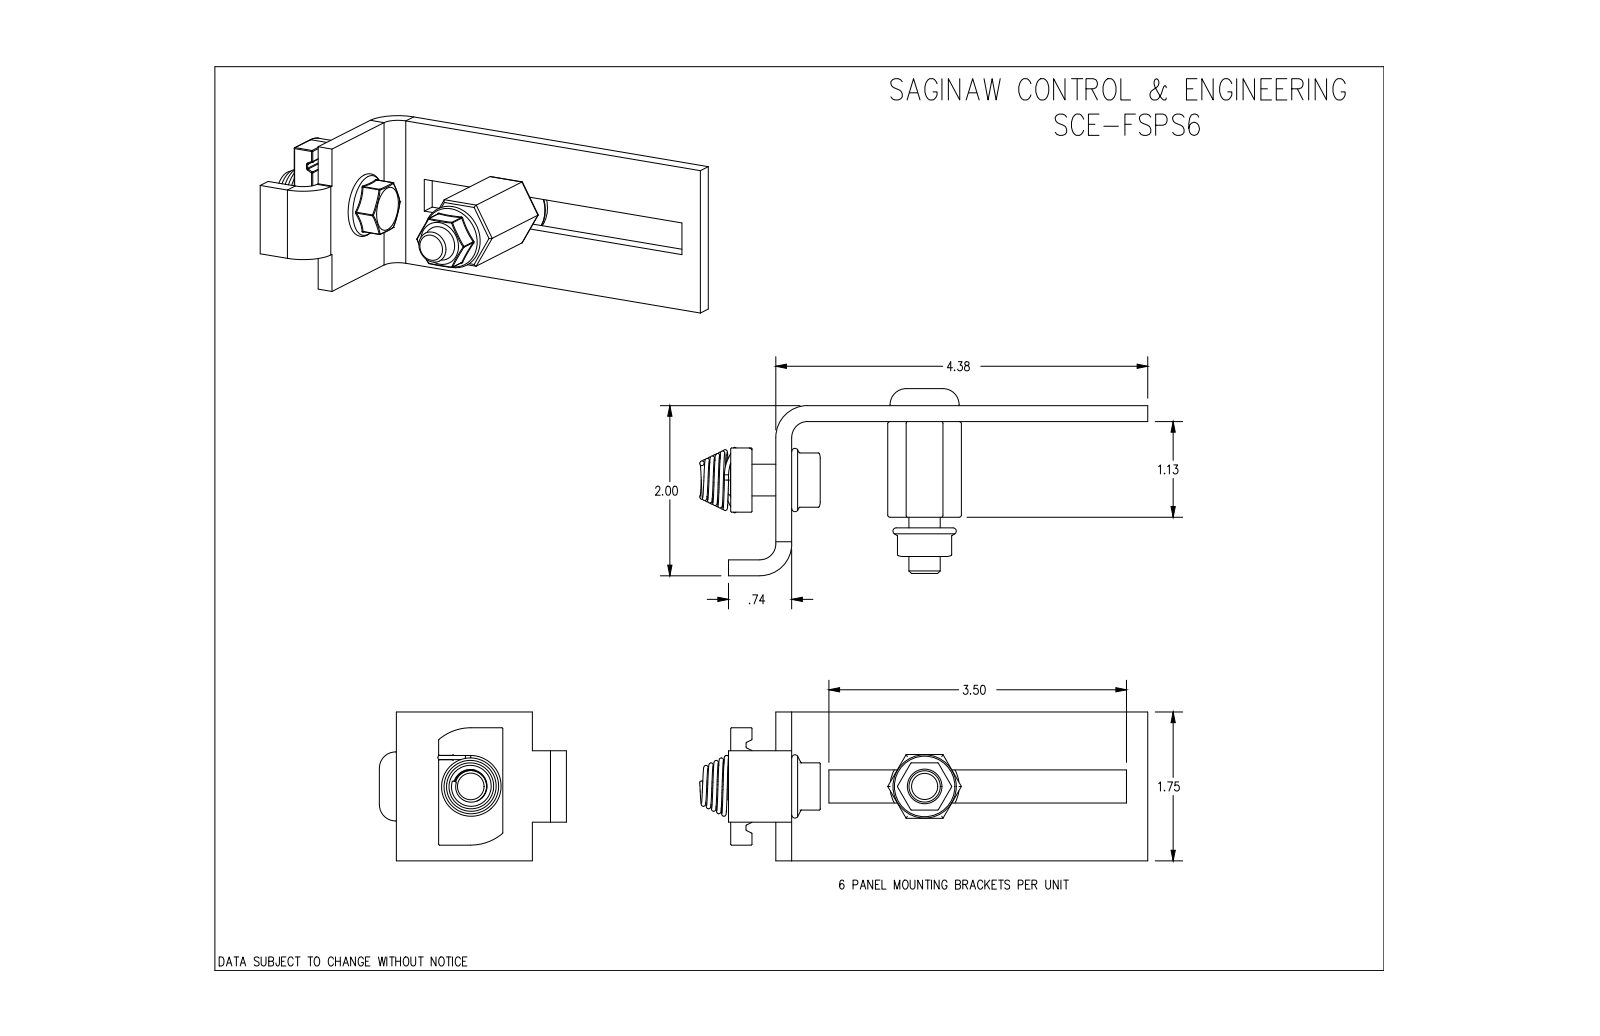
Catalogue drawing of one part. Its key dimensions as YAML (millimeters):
part_name: "SCE-FSPS6"
step_written_by: "SolidWorks 2019 (CONFIG_CONTROL_DESIGN)"
units: millimeters
bodies: {solids: 36, faces: 1632, planar: 450, cylindrical: 540, other: 642}
overall_size: [1524.1, 1207.5, 55.9]
volume: 285600
surface_area: 154300
round_holes:
  - {diameter: 9.3, count: 6}
  - {diameter: 9.5, count: 6}
  - {diameter: 9.5, count: 5}
round_bosses_or_shafts:
  - {diameter: 1.2, count: 12}
  - {diameter: 20.7, count: 6}
  - {diameter: 9.3, count: 6}
  - {diameter: 9.5, count: 3}
partial_cylinders:
  - {radius: 0.3, count: 254}
  - {radius: 0.6, count: 60}
  - {radius: 1.2, count: 24}
  - {radius: 14.7, count: 6}
  - {radius: 4.7, count: 4}
  - {radius: 4.8, count: 4}
  - {radius: 9.5, count: 4}
  - {radius: 4.7, count: 2}
face_to_face_distances: [4.7, 1157.3, 739.9, 17.3, 19.1, 1152.6, 1162.1, 12.7, 4.6, 27.2]
hole_center_spacings: [739.8, 739.9, 1073.2, 1479.7, 1303.4, 1303.5, 1827.9]
